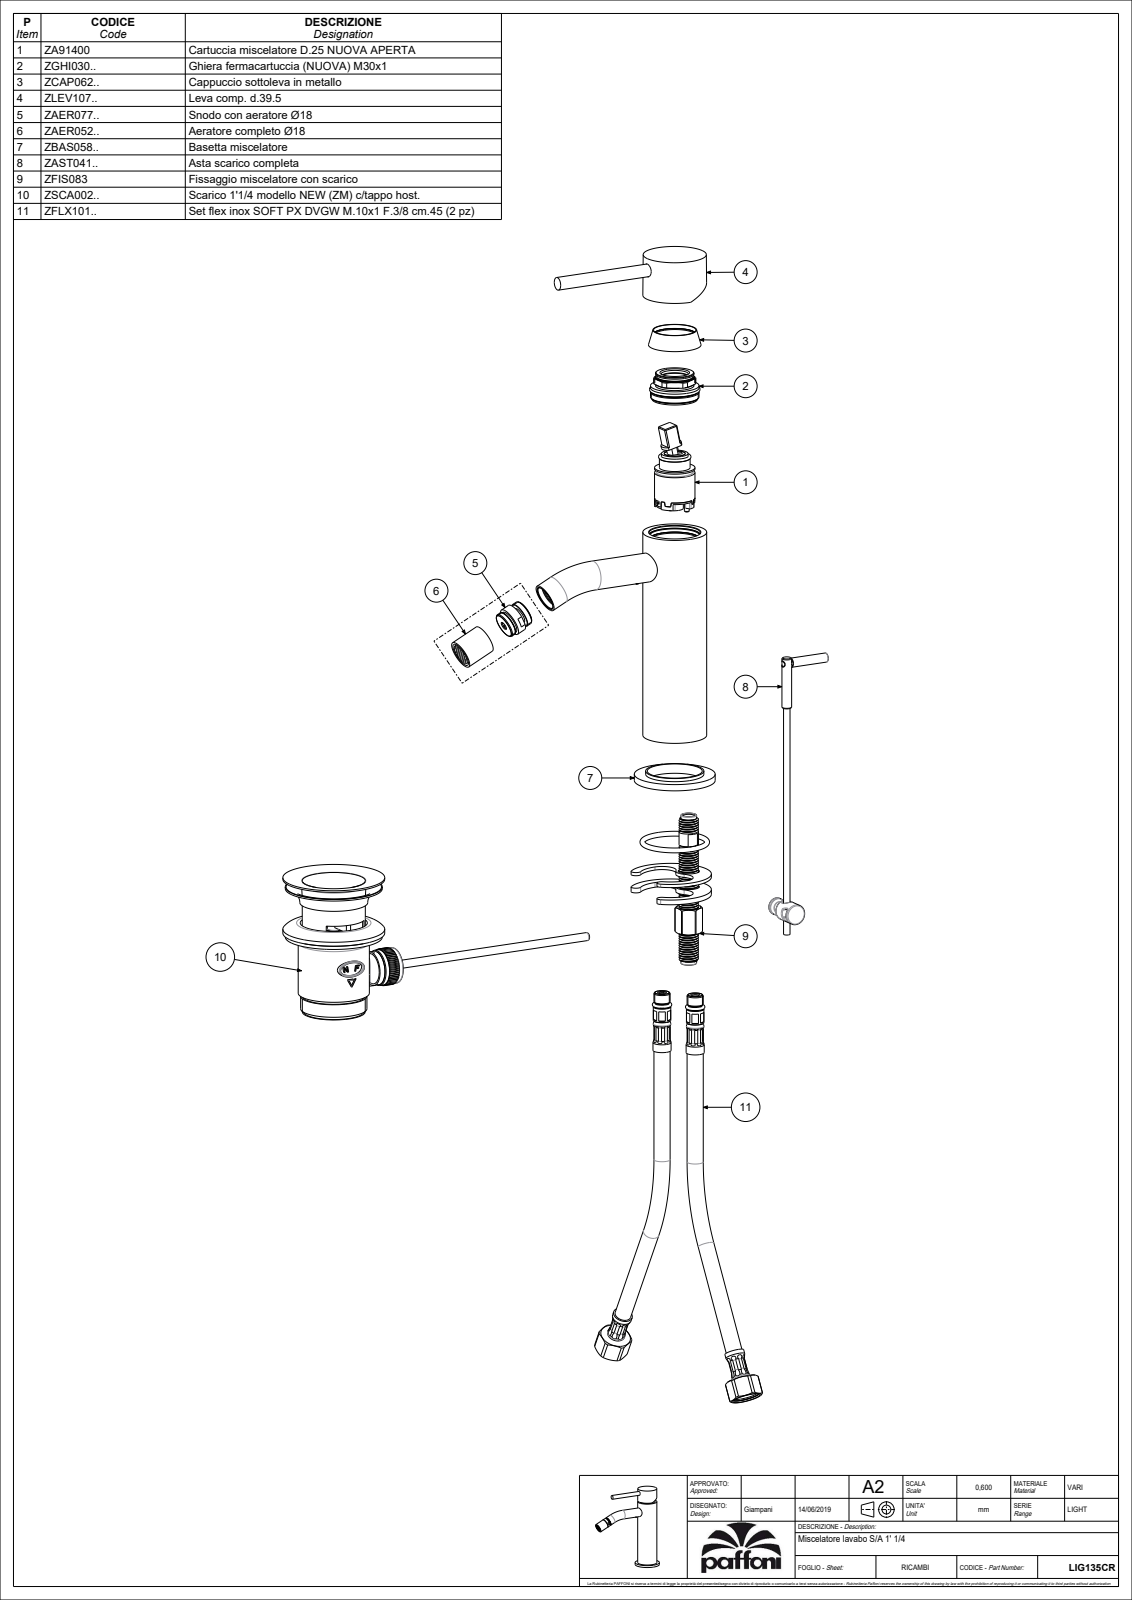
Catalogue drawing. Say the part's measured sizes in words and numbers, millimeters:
The part is named "LIG135CR". Its 3-D file was written by "CREO PARAMETRIC BY PTC INC, 2020044 (CONFIG_CONTROL_DESIGN)". It is 0 solids with 136 faces: 54 planar, 52 cylindrical and 30 other. Overall it measures 162.9 by 162.65 by 50 millimeters. Round holes: 1 of diameter 3. Round bosses or shafts: 4 of diameter 18, 2 of diameter 5.5, 1 of diameter 50, 1 of diameter 39.5, 1 of diameter 10, 1 of diameter 8, 1 of diameter 7.9, 1 of diameter 7.6. Partial cylindrical surfaces (rounded edges, fillets, slot ends): 8 of radius 1, 2 of radius 0.8, 1 of radius 3.5, 1 of radius 5, 1 of radius 6.4. The main face-to-face distances are 4, 134, 130, 10, 144, 140, 159.15, 155.15, 25.15, 15.15.
